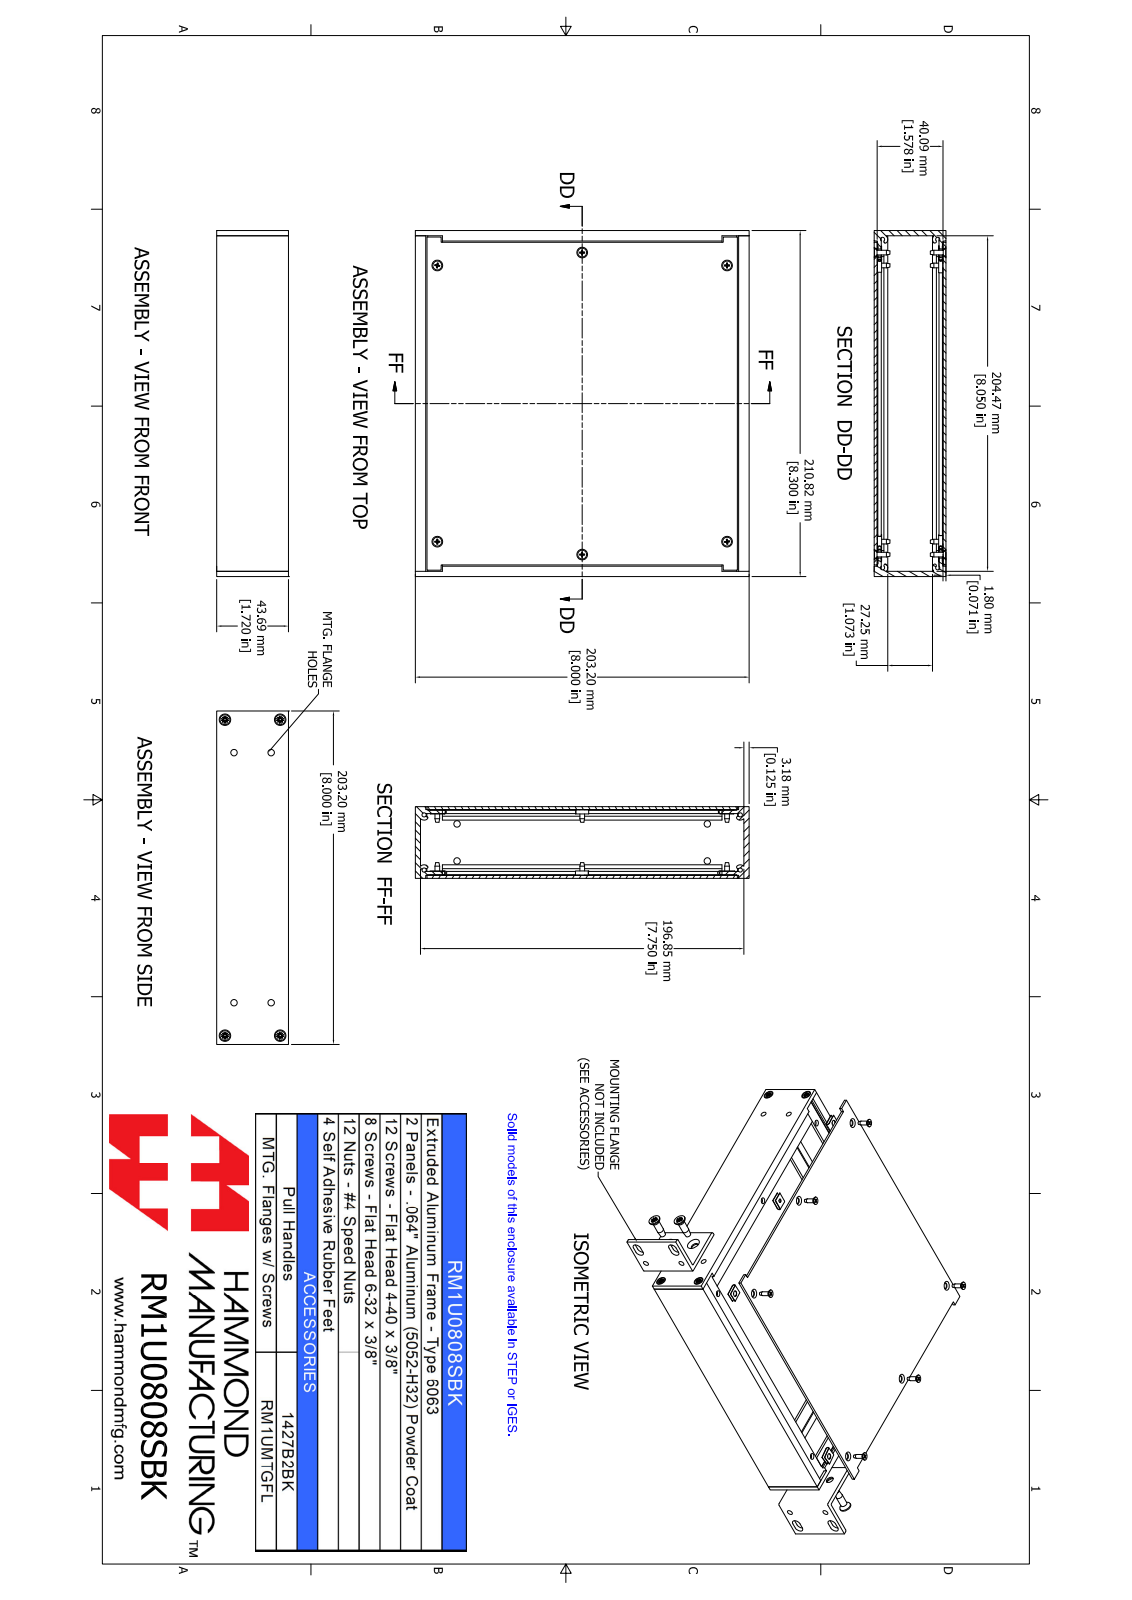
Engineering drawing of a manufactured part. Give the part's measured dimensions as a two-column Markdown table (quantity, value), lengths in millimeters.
| quantity | value |
| --- | --- |
| part name | RM1U0808SBK |
| STEP written by | SolidWorks 2021 (AUTOMOTIVE_DESIGN) |
| units | millimeters |
| bodies | 38 solids, 976 faces (468 planar, 156 cylindrical, 352 other) |
| overall size | 210.8 × 203.2 × 43.7 |
| volume | 314 100 mm³ |
| surface area | 287 900 mm² |
| round holes (diameter × count) | 2.5 × 6, 4 × 6, 4.3 × 6, 3.5 × 4, 4 × 4 |
| round bosses / shafts (diameter × count) | 5.4 × 6, 2.8 × 6, 6 × 4, 3.5 × 4 |
| partial cylindrical surfaces (radius × count) | 1 × 12, 1.2 × 12, 1.3 × 8, 3.2 × 8, 1 × 7, 0.9 × 4 |
| main face-to-face distances | 1.8, 41.9, 43.7, 40.1, 3.2, 37.6, 4.2, 39.4, 2.4, 37.2 |
| hole center spacings | 20.8, 88.5, 172.6, 22.6, 33.6, 34.5, 34.5, 152.4 |
